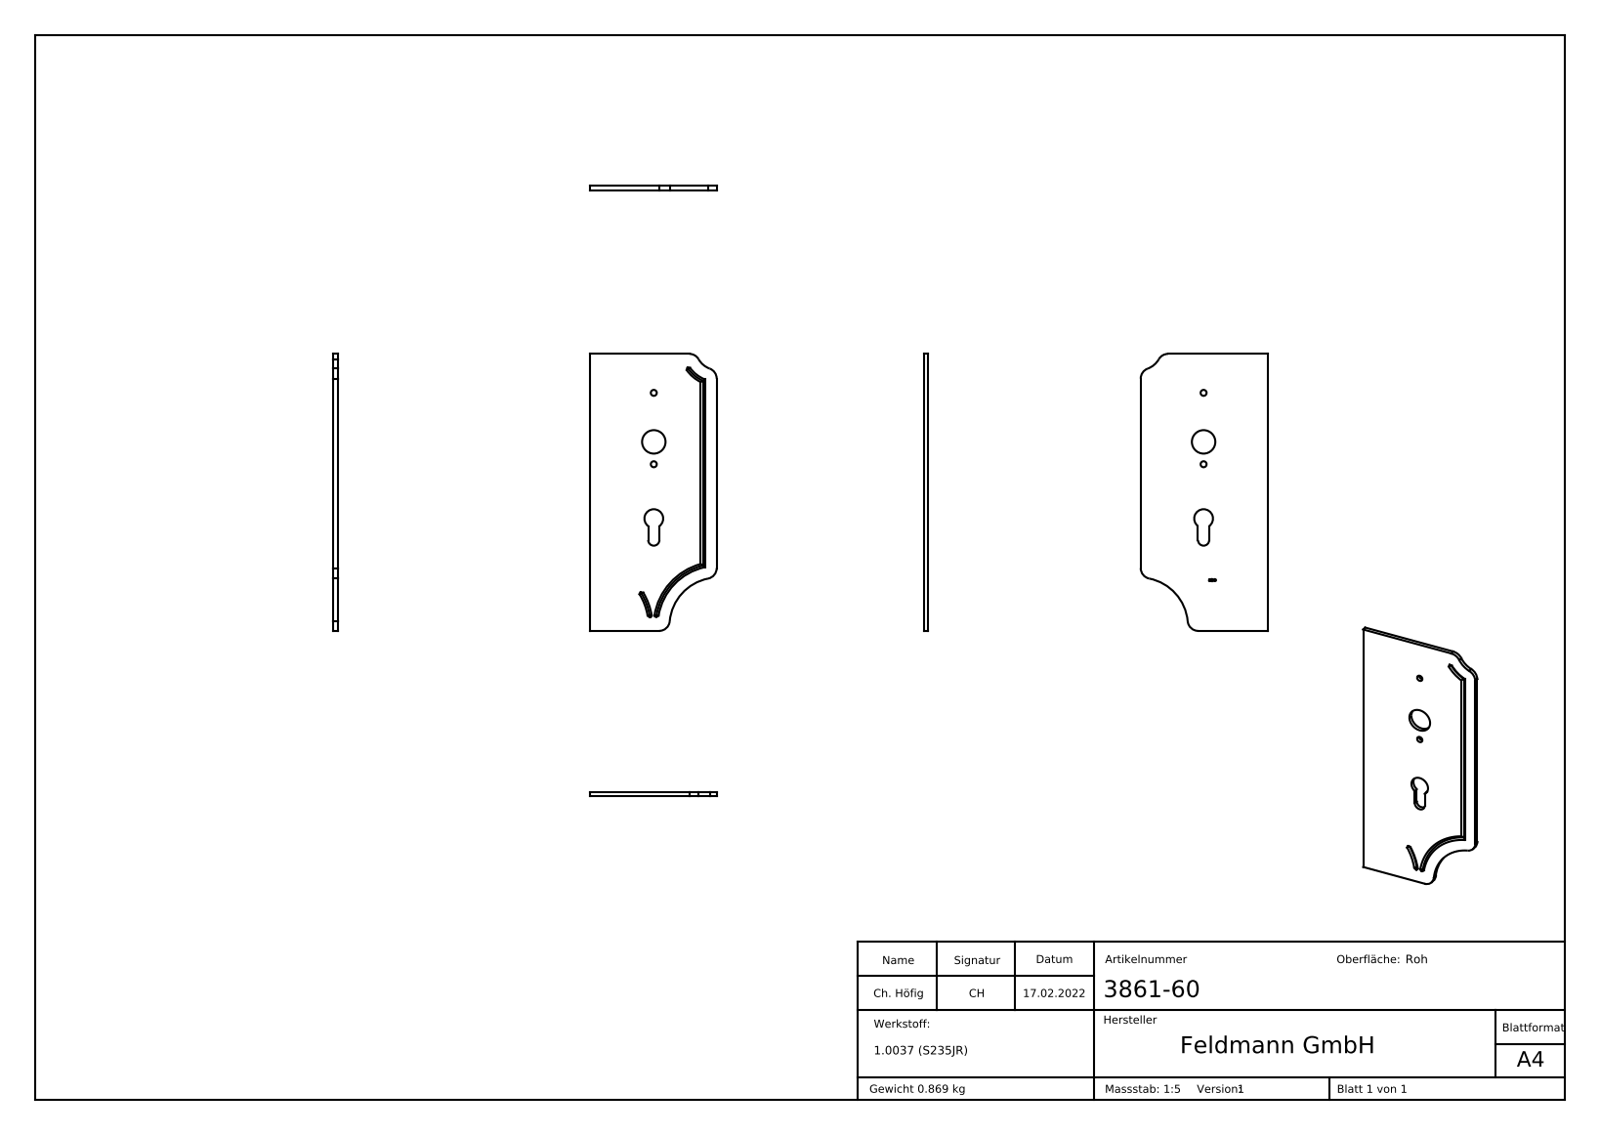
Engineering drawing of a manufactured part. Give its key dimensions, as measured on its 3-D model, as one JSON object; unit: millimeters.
{"part_name": "3861-60", "step_written_by": "SolidWorks 2018 (CONFIG_CONTROL_DESIGN)", "units": "millimeters", "bodies": {"solids": 1, "faces": 133, "planar": 43, "cylindrical": 16, "other": 74}, "overall_size": [260, 119, 4], "volume_mm3": 111365, "surface_area_mm2": 60100, "round_holes": [[5.6, 2], [17.6, 1], [22, 1]], "partial_cylinders_radius": [[10, 4], [5.25, 1], [20, 1], [45.18, 1]], "face_to_face_distances": [4, 119, 260, 54.75, 65.25, 10.5, 64.25, 53.75, 3.8, 2.22], "hole_center_spacings": [21, 46, 51, 67, 72, 118]}
